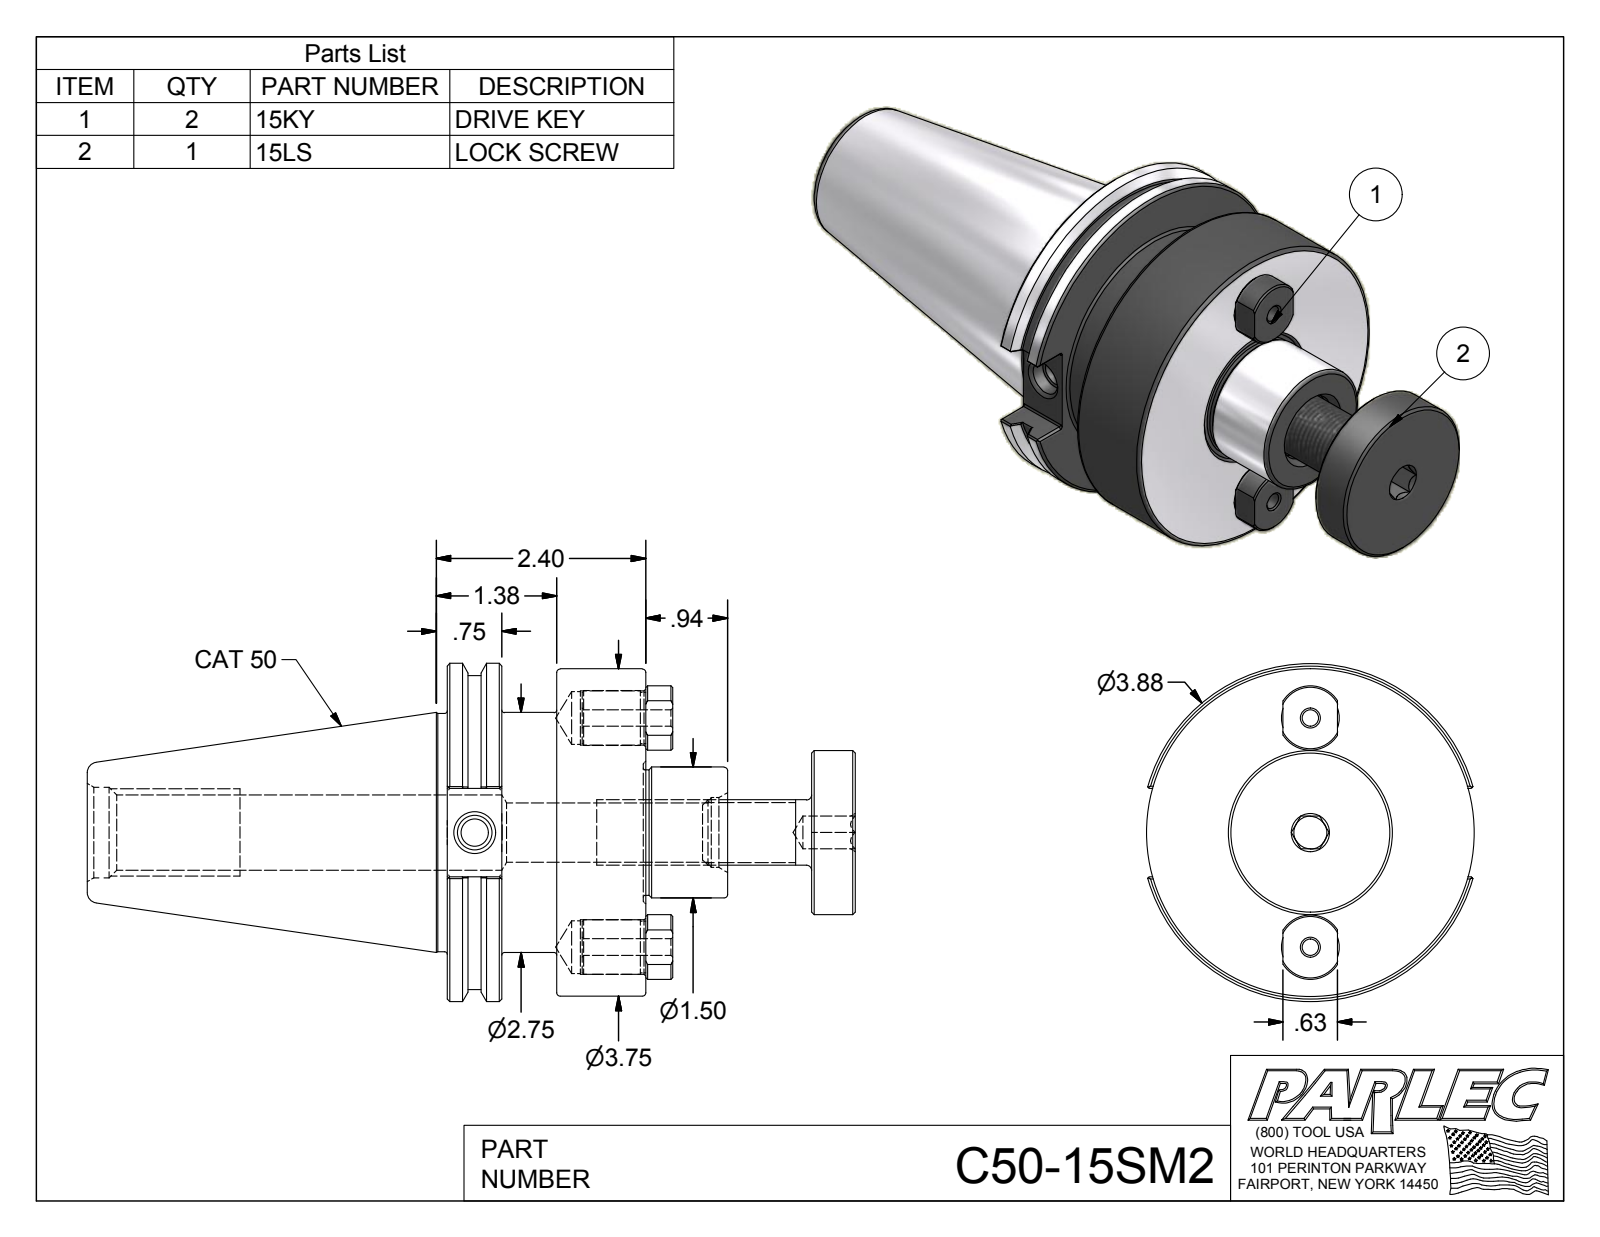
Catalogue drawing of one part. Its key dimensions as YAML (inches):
part_name: "C50-15SM2; C50-15SM2-1; 15LS; 15KY"
step_written_by: "Autodesk Inventor 2012 (AUTOMOTIVE_DESIGN)"
units: inches
bodies: {solids: 4, faces: 168, planar: 63, cylindrical: 46, other: 59}
overall_size: [8.802, 3.875, 3.75]
volume: 36.96
surface_area: 127.8
round_holes:
  - {diameter: 0.19, count: 2}
  - {diameter: 0.604, count: 2}
  - {diameter: 0.624, count: 2}
  - {diameter: 0.315, count: 1}
  - {diameter: 0.375, count: 1}
  - {diameter: 0.399, count: 1}
  - {diameter: 0.682, count: 1}
  - {diameter: 0.8, count: 1}
  - {diameter: 0.865, count: 1}
  - {diameter: 1.038, count: 1}
round_bosses_or_shafts:
  - {diameter: 0.626, count: 2}
  - {diameter: 0.59, count: 2}
  - {diameter: 3.875, count: 1}
  - {diameter: 3.75, count: 1}
  - {diameter: 3.594, count: 1}
  - {diameter: 2.75, count: 1}
  - {diameter: 2.73, count: 1}
  - {diameter: 1.88, count: 1}
partial_cylinders:
  - {radius: 0.02, count: 12}
  - {radius: 0.37, count: 2}
face_to_face_distances: [1.02, 1.255, 2.275, 0.625, 0.63, 1.65, 4.676, 4.052, 3.422, 2.402]
hole_center_spacings: [1.312, 1.312, 2.624]
